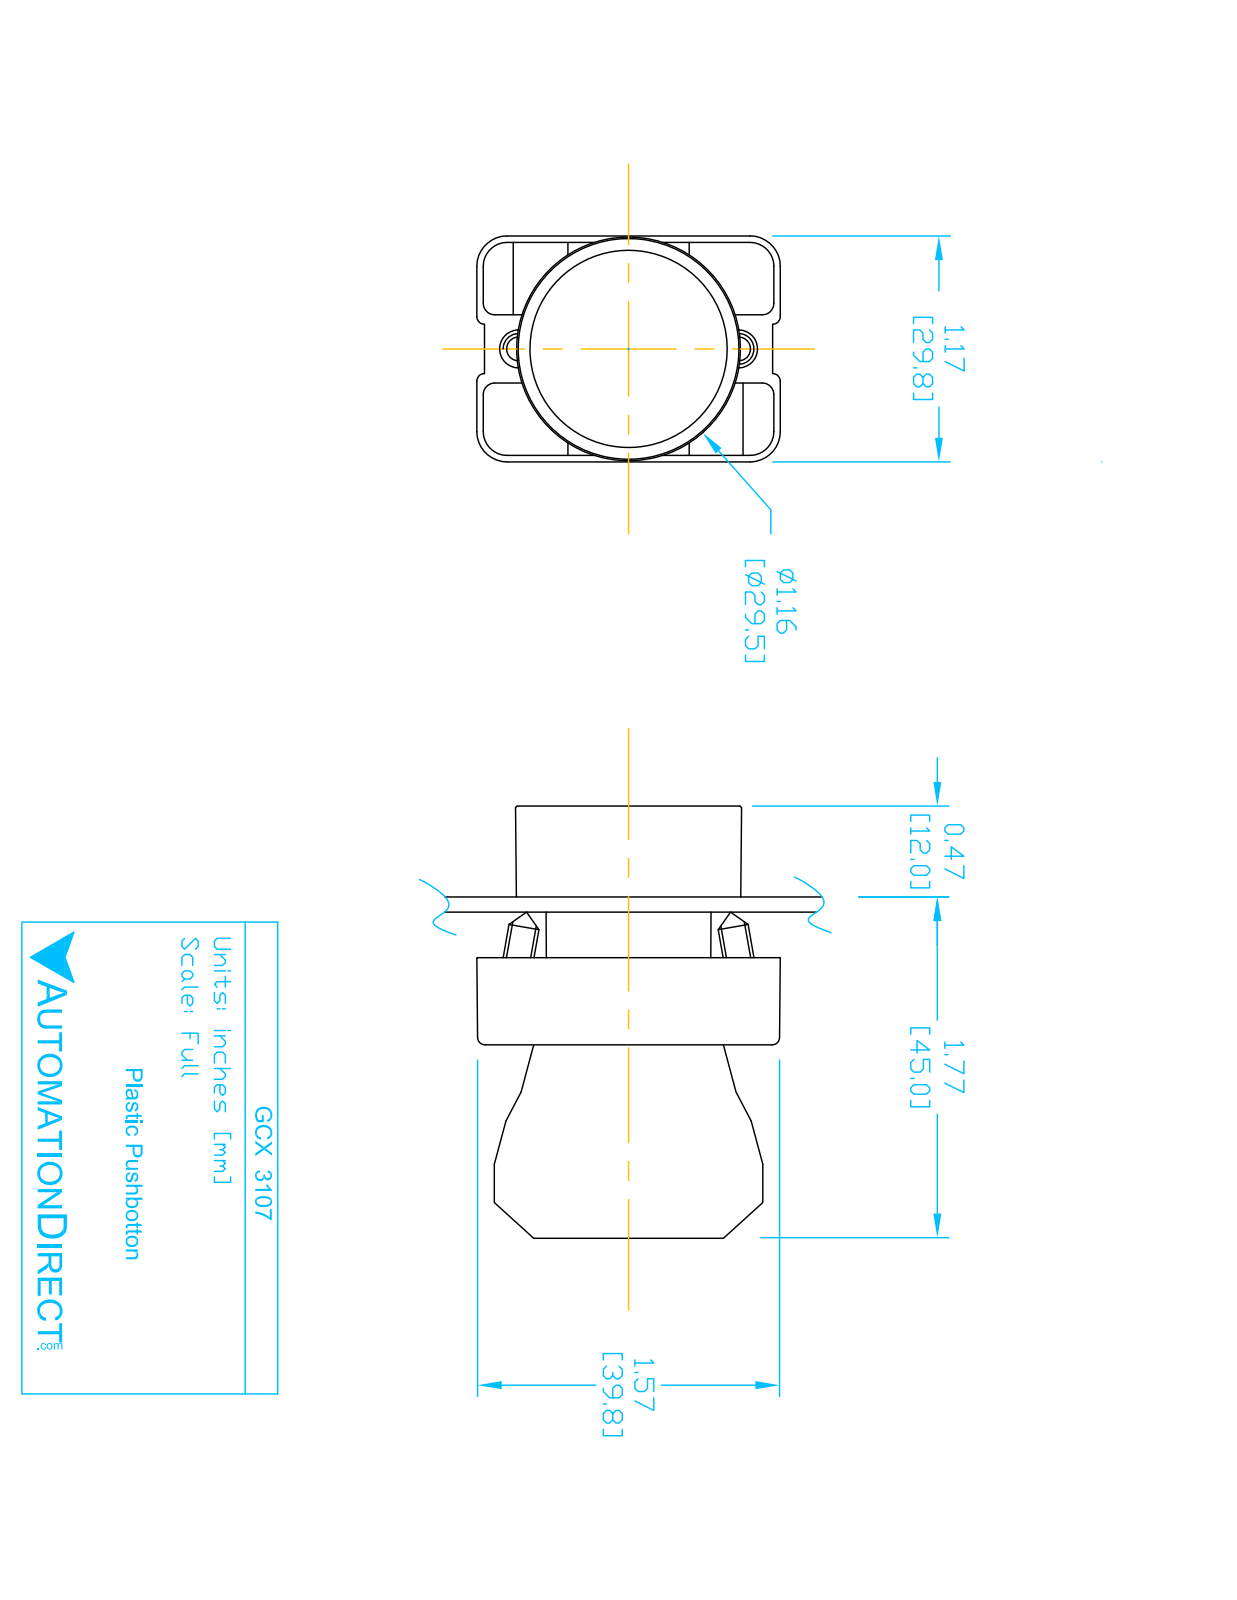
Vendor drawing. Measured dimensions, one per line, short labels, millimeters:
name: GCX3107 OPERATOR; ecx1040; ECX3029-2; GCX3107
written by: SolidWorks 2016 (AUTOMOTIVE_DESIGN)
unit: mm
bodies: 6 solids, 386 faces (227 planar, 132 cylindrical, 27 other)
size: 56.3 × 40.2 × 29.9
volume: 28 530 mm³; area: 17 510 mm²
holes: 2× ⌀2, 2× ⌀3.1, 2× ⌀3.3, 1× ⌀2.2, 1× ⌀5, 1× ⌀22.3, 1× ⌀22.6, 1× ⌀26
bosses: 2× ⌀4, 1× ⌀29.8, 1× ⌀25.5, 1× ⌀24, 1× ⌀21.7, 1× ⌀19.8
rounds: 24× R1.5, 12× R1, 12× R3.1, 12× R4, 4× R1, 2× R3.3, 1× R0.5, 1× R1.6
face distances: 18.3, 14.7, 0.8, 12, 30.3, 0.8, 17.5, 15.2, 29.5, 27.2
hole spacings: 6, 13.8, 12, 12.4
